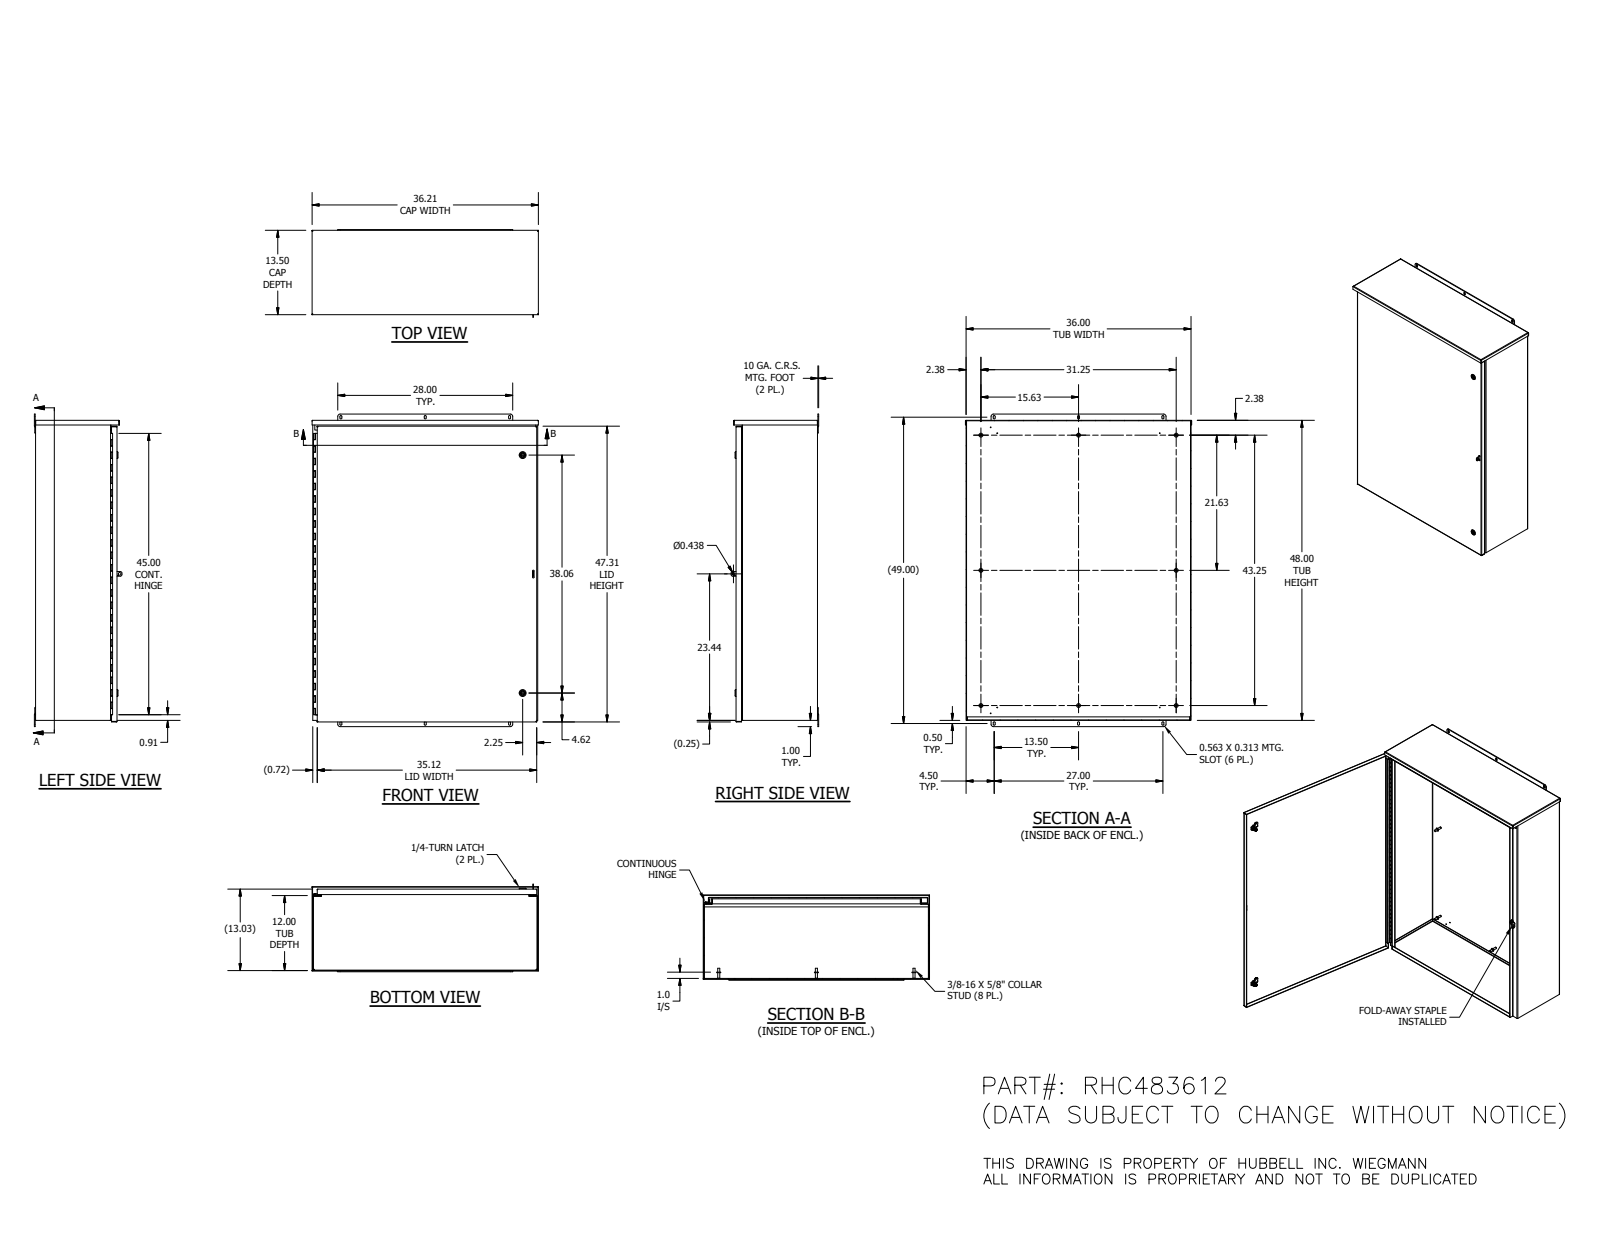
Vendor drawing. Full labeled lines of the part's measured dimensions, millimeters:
Part name (STEP PRODUCT): RHC483612BLR; RHC36TOP; RHC3612BTM; RHC4836LID (+8 more)
STEP written by: Autodesk Inventor 2016 (AUTOMOTIVE_DESIGN)
Units: millimetres
Bodies: 34 solids, 1664 faces (951 planar, 561 cylindrical, 152 other)
Overall size (bounding box): 1270 × 919.75 × 355.9
Volume: 7 784 000 mm³ · Surface area: 8 198 000 mm²
Round holes (diameter × count): ⌀3.05 ×7, ⌀3.17 ×2, ⌀5 ×2, ⌀8 ×2, ⌀10 ×2, ⌀10.2 ×2, ⌀16.1 ×2, ⌀20.38 ×2, ⌀5.03 ×1, ⌀5.11 ×1, ⌀11.11 ×1
Round bosses / shafts (diameter × count): ⌀15.88 ×8, ⌀8.38 ×8, ⌀28 ×2, ⌀27 ×2, ⌀23 ×2, ⌀19.8 ×2, ⌀15.8 ×2, ⌀15.2 ×2
Partial cylindrical surfaces — rounded edges, fillets, slot ends (radius × count): R0.3 ×56, R0.5 ×21, R3.47 ×13, R3.97 ×12, R3.17 ×10, R1.59 ×9, R0.79 ×8, R2.67 ×8
Main face-to-face distances: 1.88, 329.17, 331.05, 327.29, 912.52, 1217.32, 910.64, 914.4, 1215.44, 1219.2
Hole centre spacings: 35.91, 660.4, 687.74, 1114.55, 1138.62, 1295.51, 1329.72, 8.98
